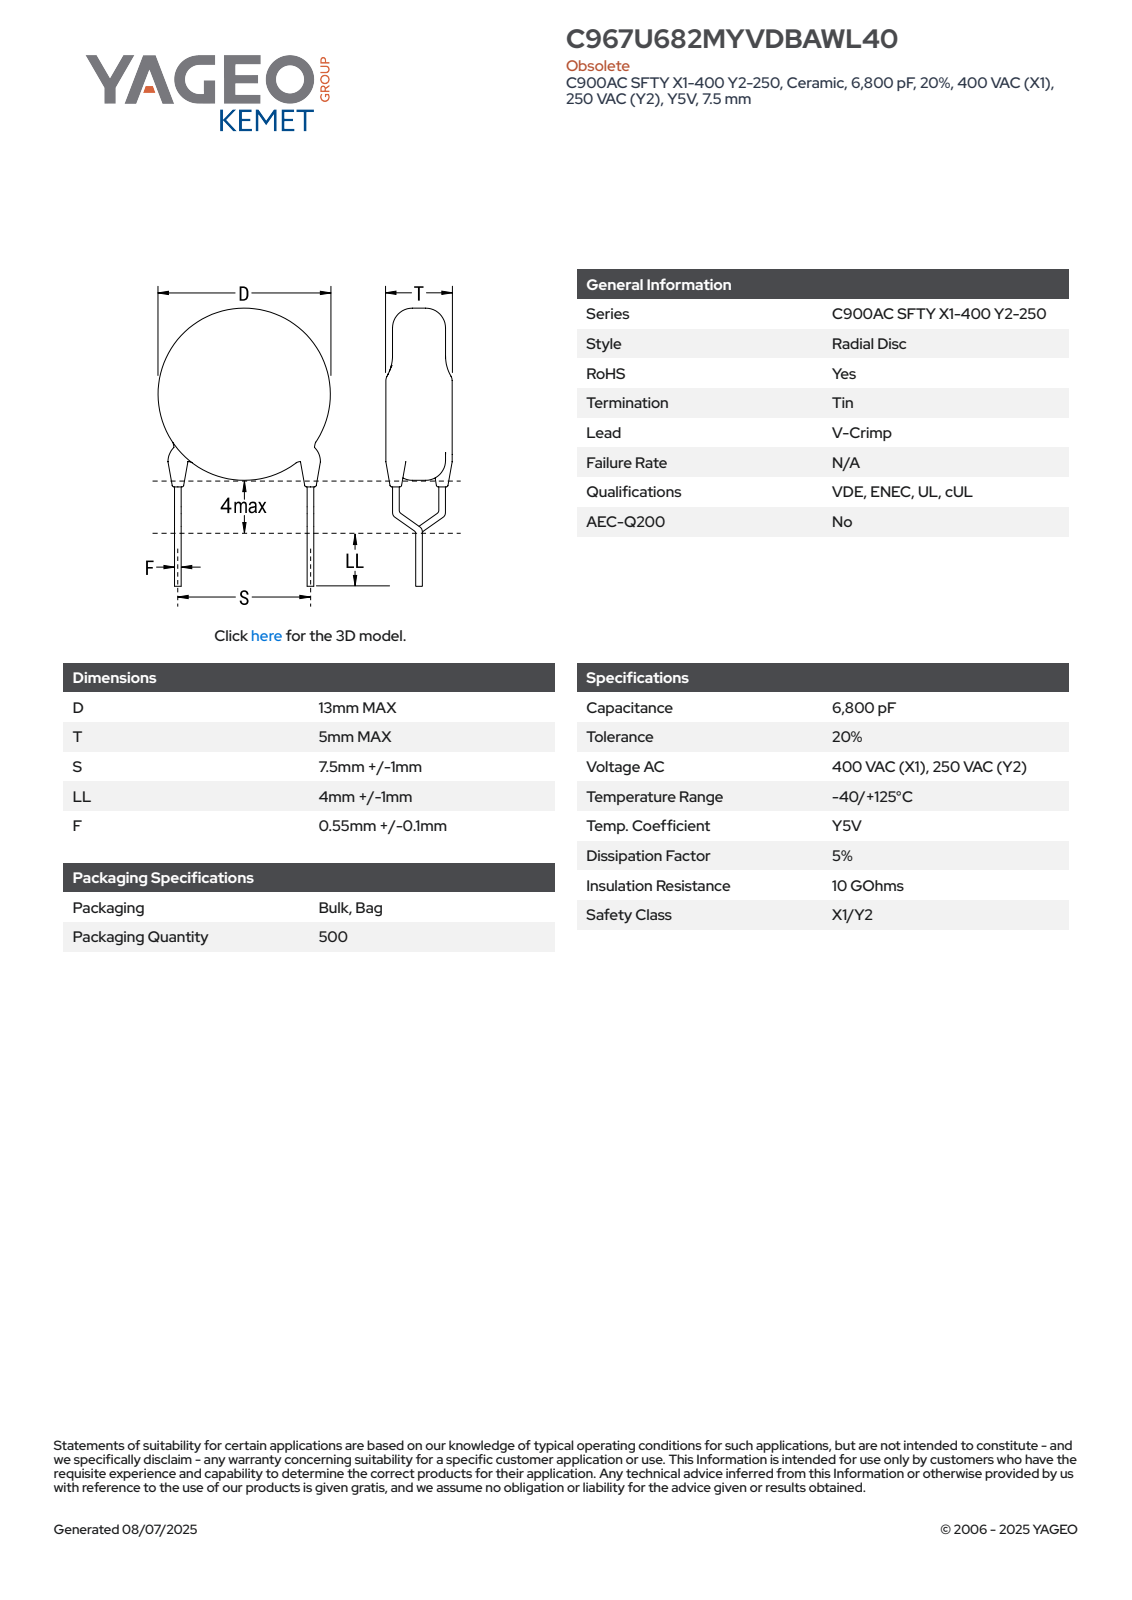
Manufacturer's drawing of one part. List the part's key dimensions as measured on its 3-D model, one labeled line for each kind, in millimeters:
Part name (STEP PRODUCT): CCD_VCC900_D13T5S7.5LL5F0.65
STEP written by: SolidWorks 2014 (AUTOMOTIVE_DESIGN)
Units: millimetres
Bodies: 5 solids, 93 faces (65 planar, 16 cylindrical, 12 other)
Overall size (bounding box): 21.8 × 13 × 5
Volume: 655 mm³ · Surface area: 495 mm²
Round bosses / shafts (diameter × count): ⌀0.65 ×6, ⌀13 ×1
Main face-to-face distances: 5, 7.9, 16.14, 8.24, 14.45, 6.55, 1.69, 0.46, 6.9, 0.63
